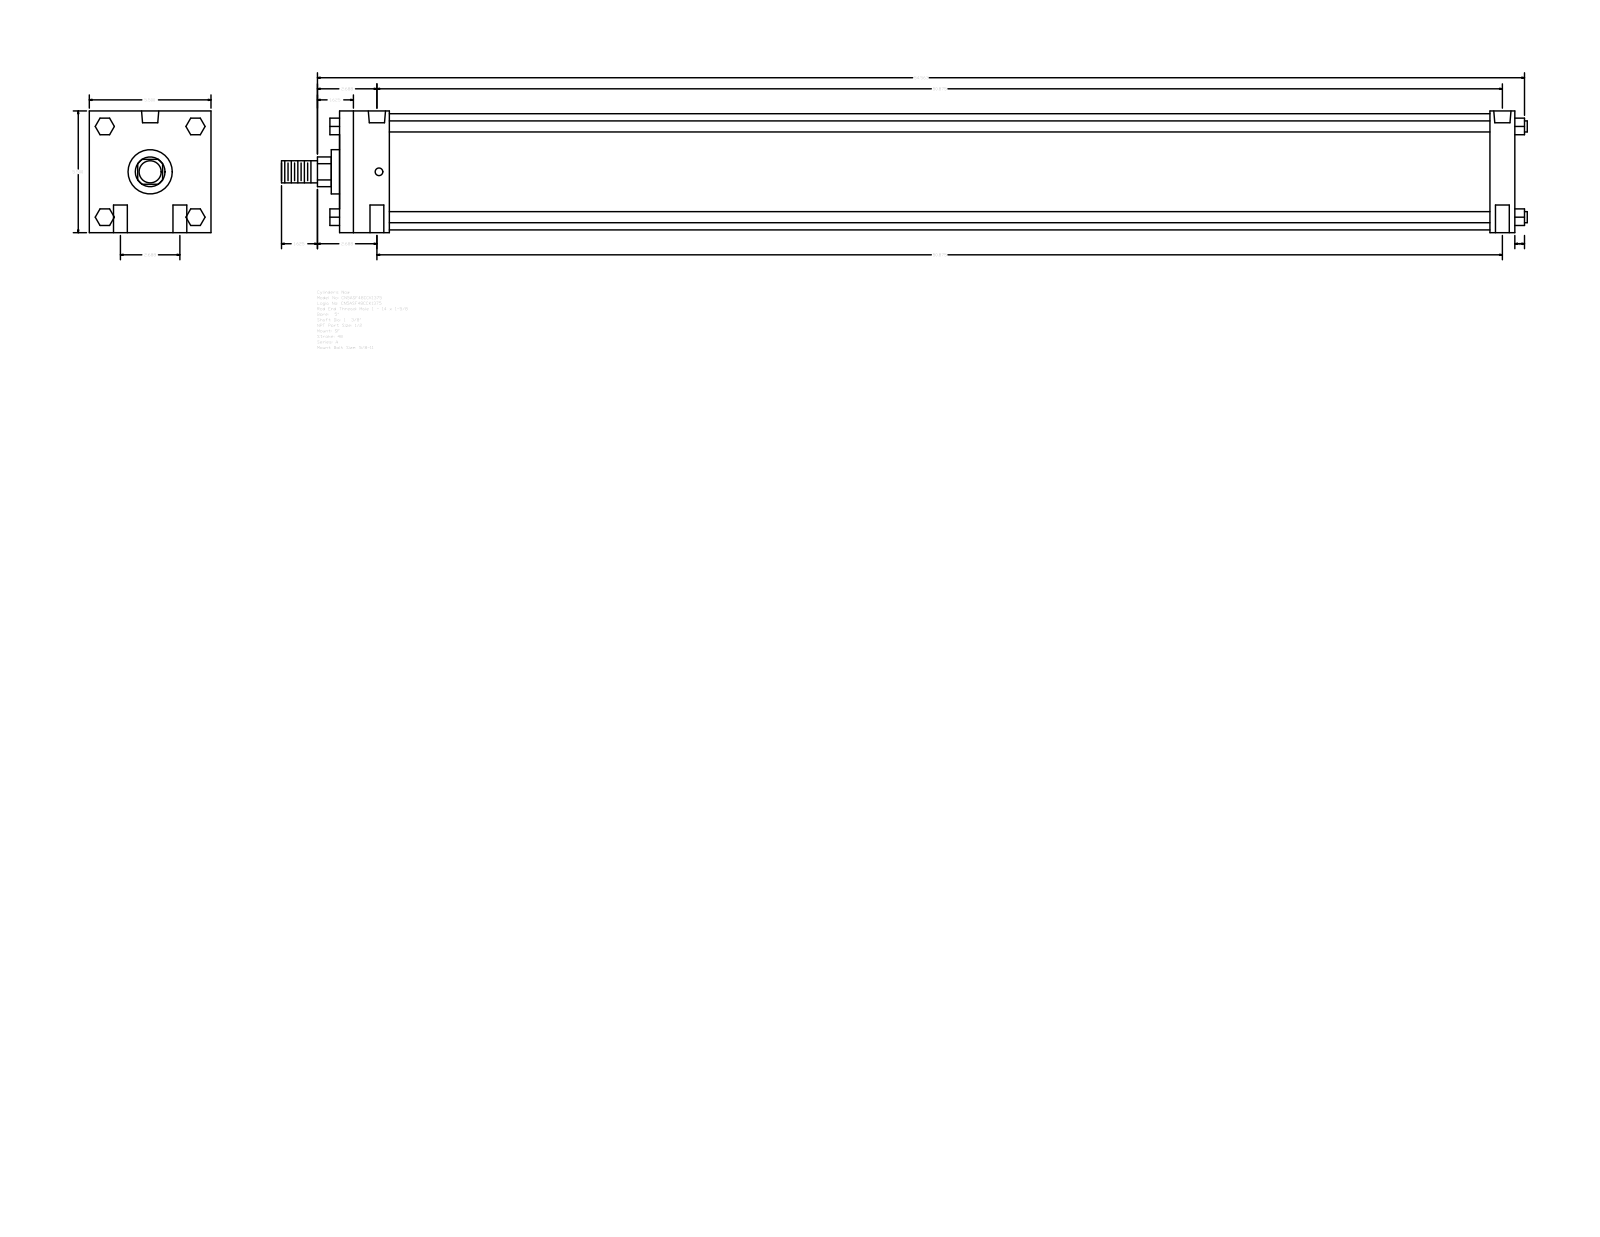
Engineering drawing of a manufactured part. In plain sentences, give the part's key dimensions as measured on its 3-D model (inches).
The part is named "A_SF__0500_1.375". Its 3-D file was written by "GSSL Pune (CONFIG_CONTROL_DESIGN)". It is 0 solids with 124 faces: 94 planar, 30 cylindrical and 0 other. Overall it measures 56.313 by 5.5 by 5.5 inches. Round holes: 4 of diameter 0.625, 2 of diameter 0.344, 2 of diameter 0.778. Round bosses or shafts: 4 of diameter 0.5, 1 of diameter 5.25, 1 of diameter 2, 1 of diameter 1.375, 1 of diameter 1. Partial cylindrical surfaces (rounded edges, fillets, slot ends): 1 of radius 0.672. The main face-to-face distances are 5.5, 53.125, 2.25, 1.125, 52, 49.75, 50.875, 0.75, 2.05, 3.55. The hole center spacings are 1.344, 50.893, 50.875, 2.687, 50.946, 50.687.
